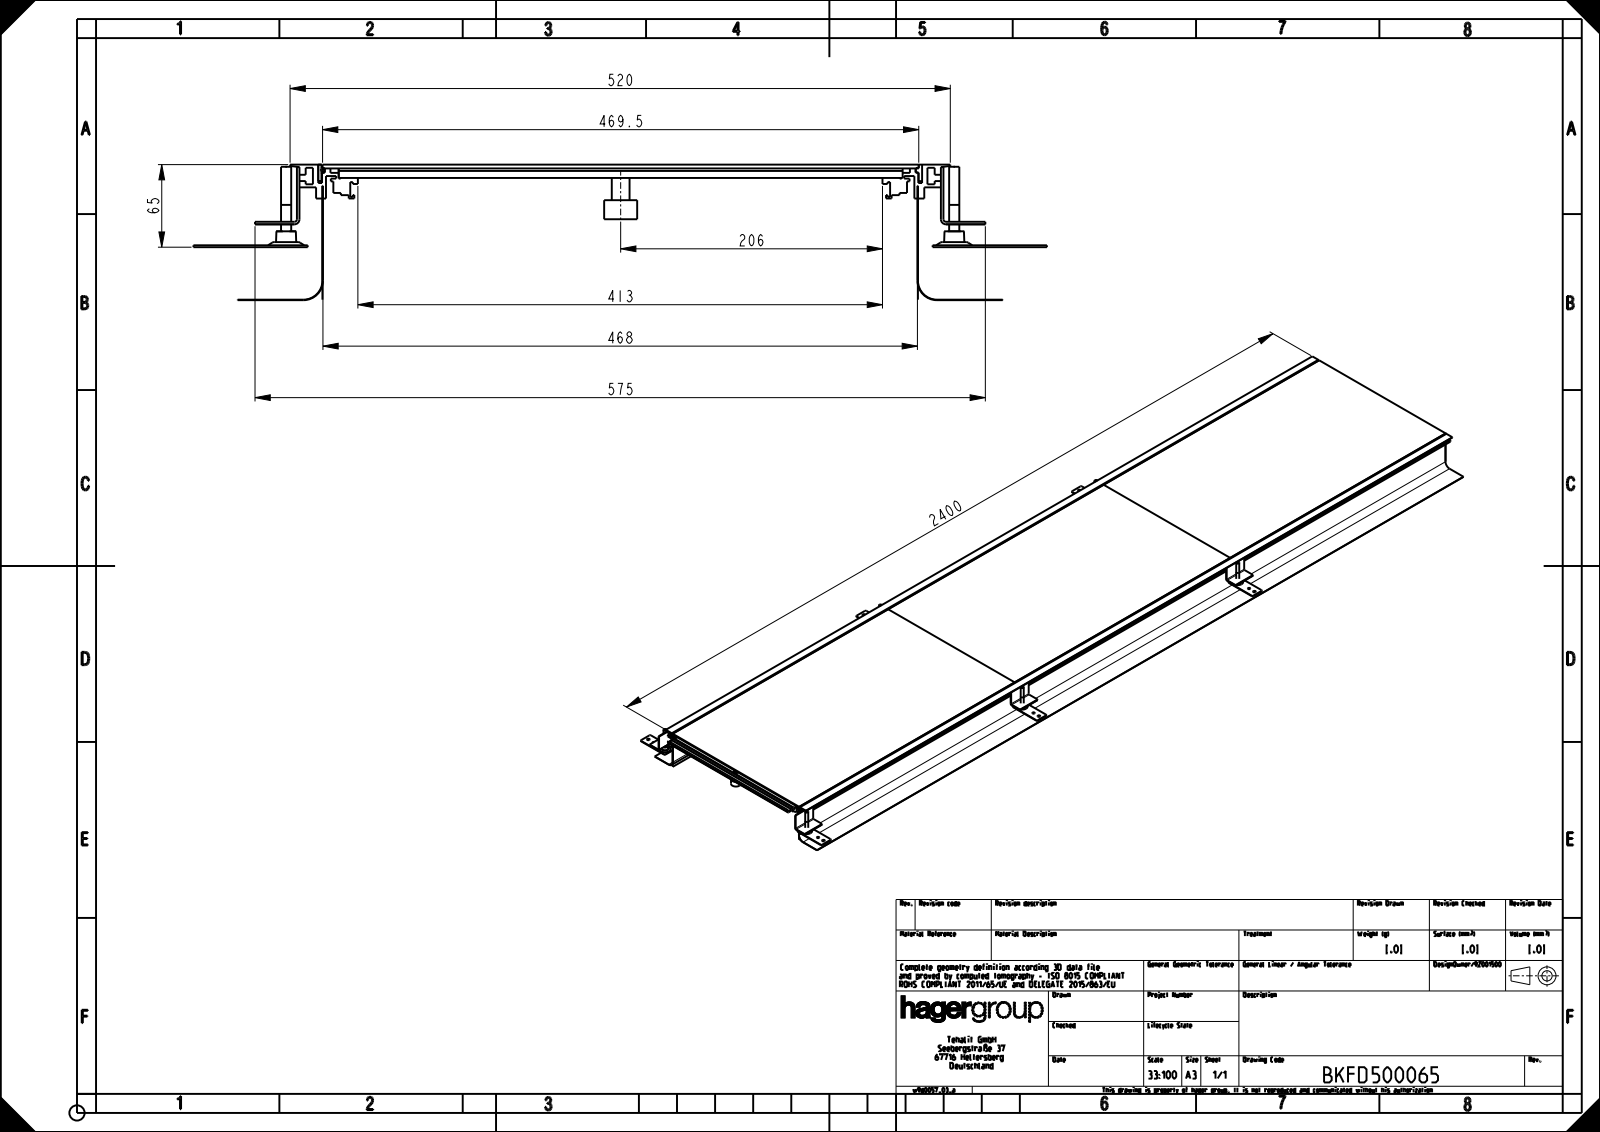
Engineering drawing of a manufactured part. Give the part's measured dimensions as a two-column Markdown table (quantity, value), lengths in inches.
| quantity | value |
| --- | --- |
| part name | U05644KUN; U05650KUN; U05647KUN; U05826KUN (+8 more) |
| STEP written by | CREO PARAMETRIC BY PTC INC, 2020281 (AUTOMOTIVE_DESIGN) |
| units | inches |
| bodies | 62 solids, 1026 faces (600 planar, 354 cylindrical, 72 other) |
| overall size | 95.768 × 26.462 × 4.201 |
| volume | 485.4 in³ |
| surface area | 9 447 in² |
| round holes (diameter × count) | 0.276 × 15, 0.315 × 9, 0.394 × 9, 0.236 × 6, 0.335 × 6, 0.453 × 6, 0.689 × 6, 0.906 × 6 |
| round bosses / shafts (diameter × count) | 1.024 × 9, 0.551 × 9, 0.469 × 9, 0.787 × 6, 0.315 × 6 |
| partial cylindrical surfaces (radius × count) | 0.079 × 92, 0.118 × 24, 0.02 × 20, 0.157 × 2, 0.591 × 2, 0.606 × 2 |
| main face-to-face distances | 0.118, 0.016, 18.447, 0.256, 0.295, 4.083, 4.201, 4.067, 4.185, 3.787 |
| hole center spacings | 31.496, 62.992, 31.506, 31.539, 31.591, 38.63, 39.091, 40.093 |
